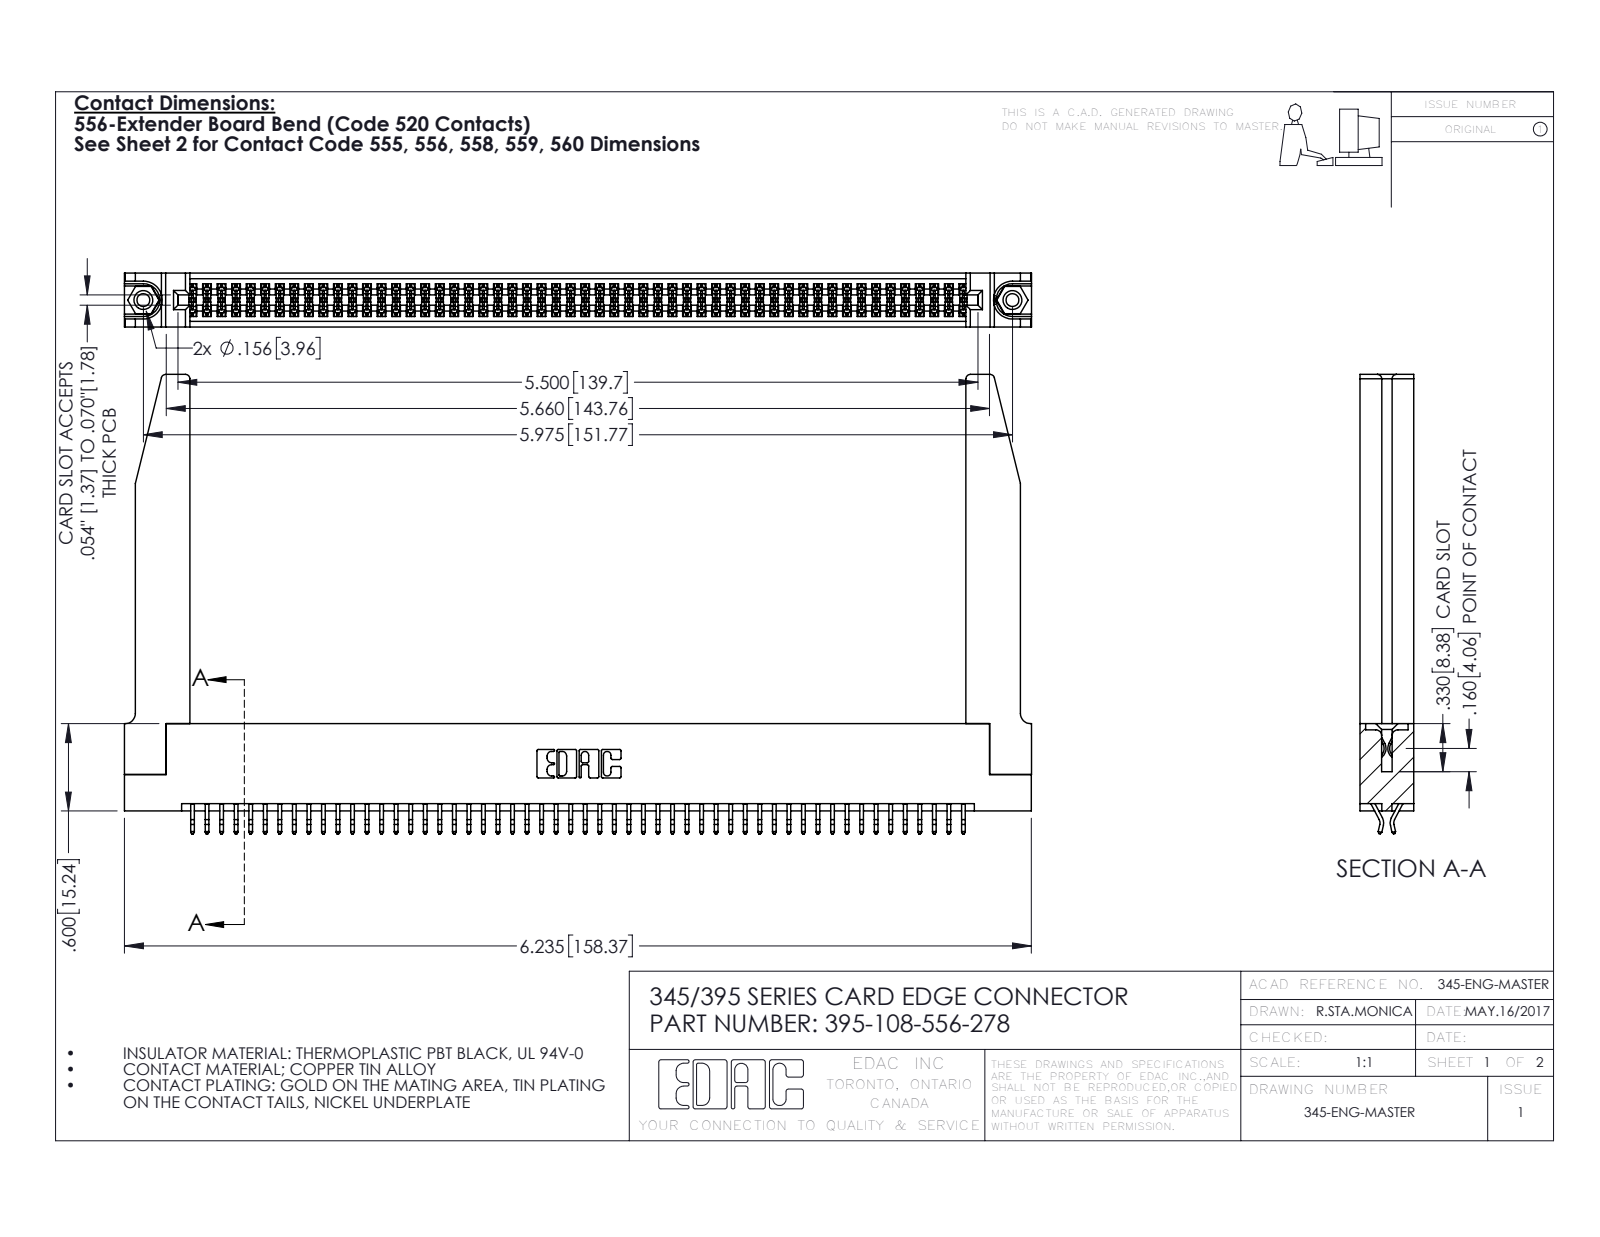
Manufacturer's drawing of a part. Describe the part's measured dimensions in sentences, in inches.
The part is named "345-292-001_556 Tail; 345-220-078_345-220-078; 345 Part_Flush Mounting Lugs - 0.156 Dia-TH; 395-108-556-278 (+1 more)". Its 3-D file was written by "SolidWorks 2016 (CONFIG_CONTROL_DESIGN)". It is 113 solids with 6408 faces: 4218 planar, 2138 cylindrical and 52 other. Overall it measures 6.236 by 3.157 by 0.37 inches. Its volume is 1.42 cubic inches and its surface area 46.31 square inches. Round holes: 2 of diameter 0.089, 2 of diameter 0.125, 2 of diameter 0.156, 1 of diameter 0.064. Round bosses or shafts: 2 of diameter 0.155. Partial cylindrical surfaces (rounded edges, fillets, slot ends): 162 of radius 0.006, 22 of radius 0.01, 8 of radius 0.03, 6 of radius 0.007, 6 of radius 0.031, 3 of radius 0.026, 2 of radius 0.01, 2 of radius 0.014. The main face-to-face distances are 0.072, 0.37, 0.298, 0.2, 0.025, 0.098, 0.272, 0.225, 0.175, 0.148. The hole center spacings are 0.27, 5.739, 5.975.
